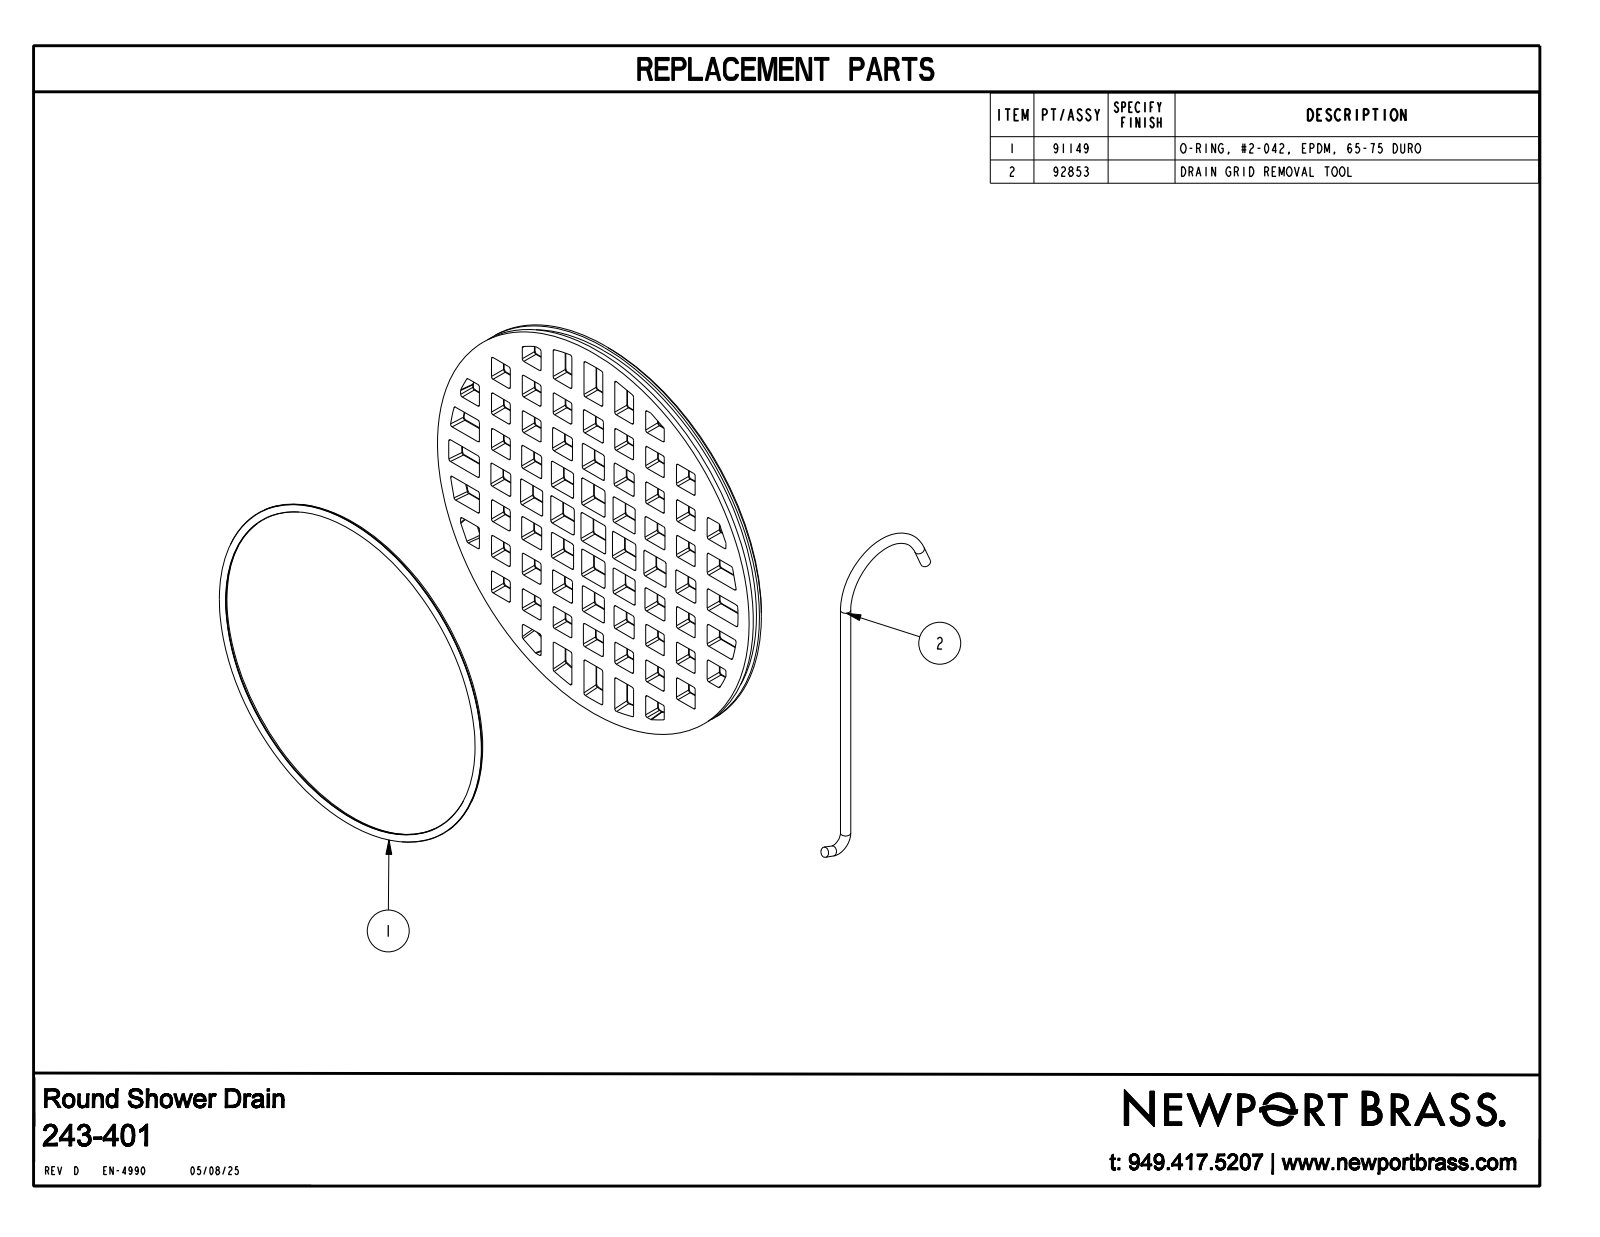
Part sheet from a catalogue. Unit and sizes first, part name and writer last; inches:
Units: inches
Overall size (bounding box): 4.04 × 4.04 × 0.188
Round bosses / shafts (diameter × count): ⌀4.04 ×1, ⌀3.962 ×1
Partial cylindrical surfaces — rounded edges, fillets, slot ends (radius × count): R0.02 ×344, R1.875 ×1
Main face-to-face distances: 0.399, 0.188, 0.798, 1.196, 1.595, 1.994, 0.407, 0.391, 0.022, 0.377
Volume: 1.367 in³ · Surface area: 62.21 in²
Bodies: 1 solid, 2294 faces (536 planar, 1066 cylindrical, 692 other)
Part name (STEP PRODUCT): 50995; 243-401_ASM
STEP written by: CREO PARAMETRIC BY PTC INC, 2018400 (CONFIG_CONTROL_DESIGN)
